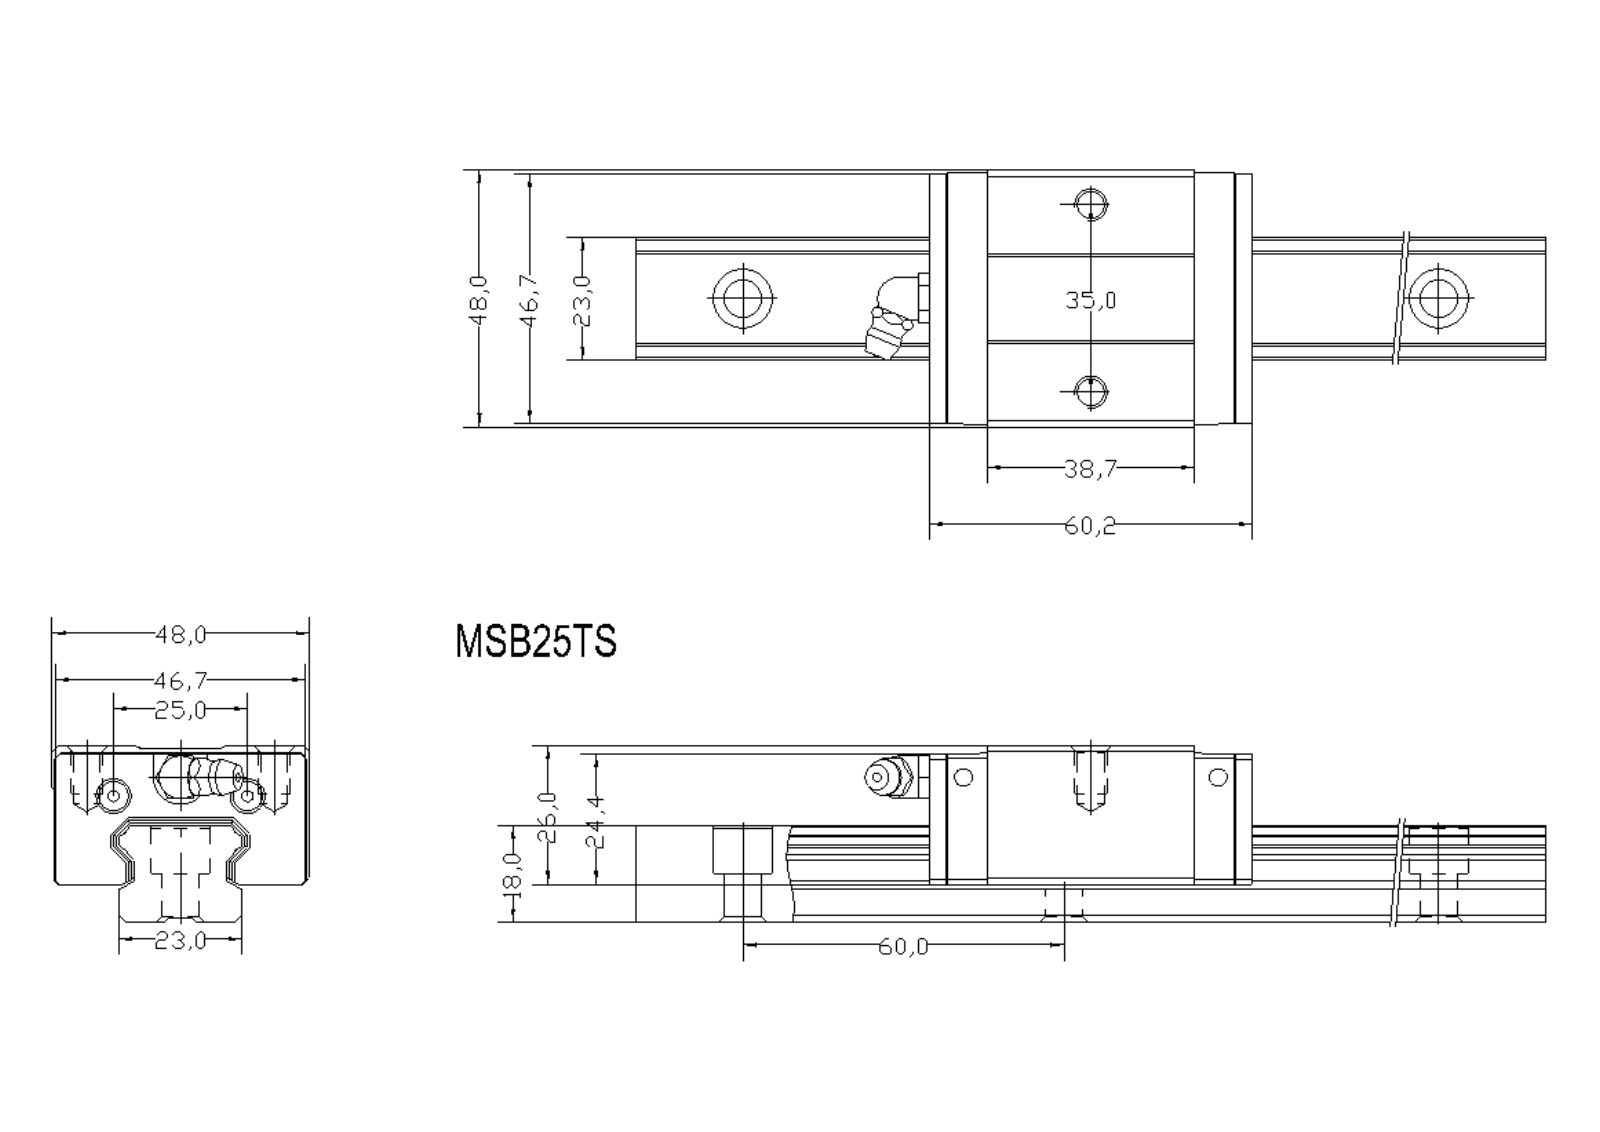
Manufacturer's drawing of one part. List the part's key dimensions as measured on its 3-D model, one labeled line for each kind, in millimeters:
STEP written by: Kubotek KeyCreator V6.5.2 (0407) (CONFIG_CONTROL_DESIGN)
Units: millimetres
Bodies: 3 solids, 192 faces (123 planar, 48 cylindrical, 21 other)
Overall size (bounding box): 220 × 48 × 33
Volume: 133 024 mm³ · Surface area: 35 379 mm²
Round holes (diameter × count): ⌀7 ×4, ⌀11 ×4, ⌀6.5 ×3, ⌀6 ×2
Round bosses / shafts (diameter × count): ⌀8 ×1
Partial cylindrical surfaces — rounded edges, fillets, slot ends (radius × count): R2.2 ×4, R1 ×2, R5.05 ×1
Main face-to-face distances: 18, 2.8, 20.2, 17.4, 7, 11, 12.5, 15.3, 32.7, 35.5
Hole centre spacings: 34.73, 91.69, 60, 12.98, 120, 25, 35, 180
